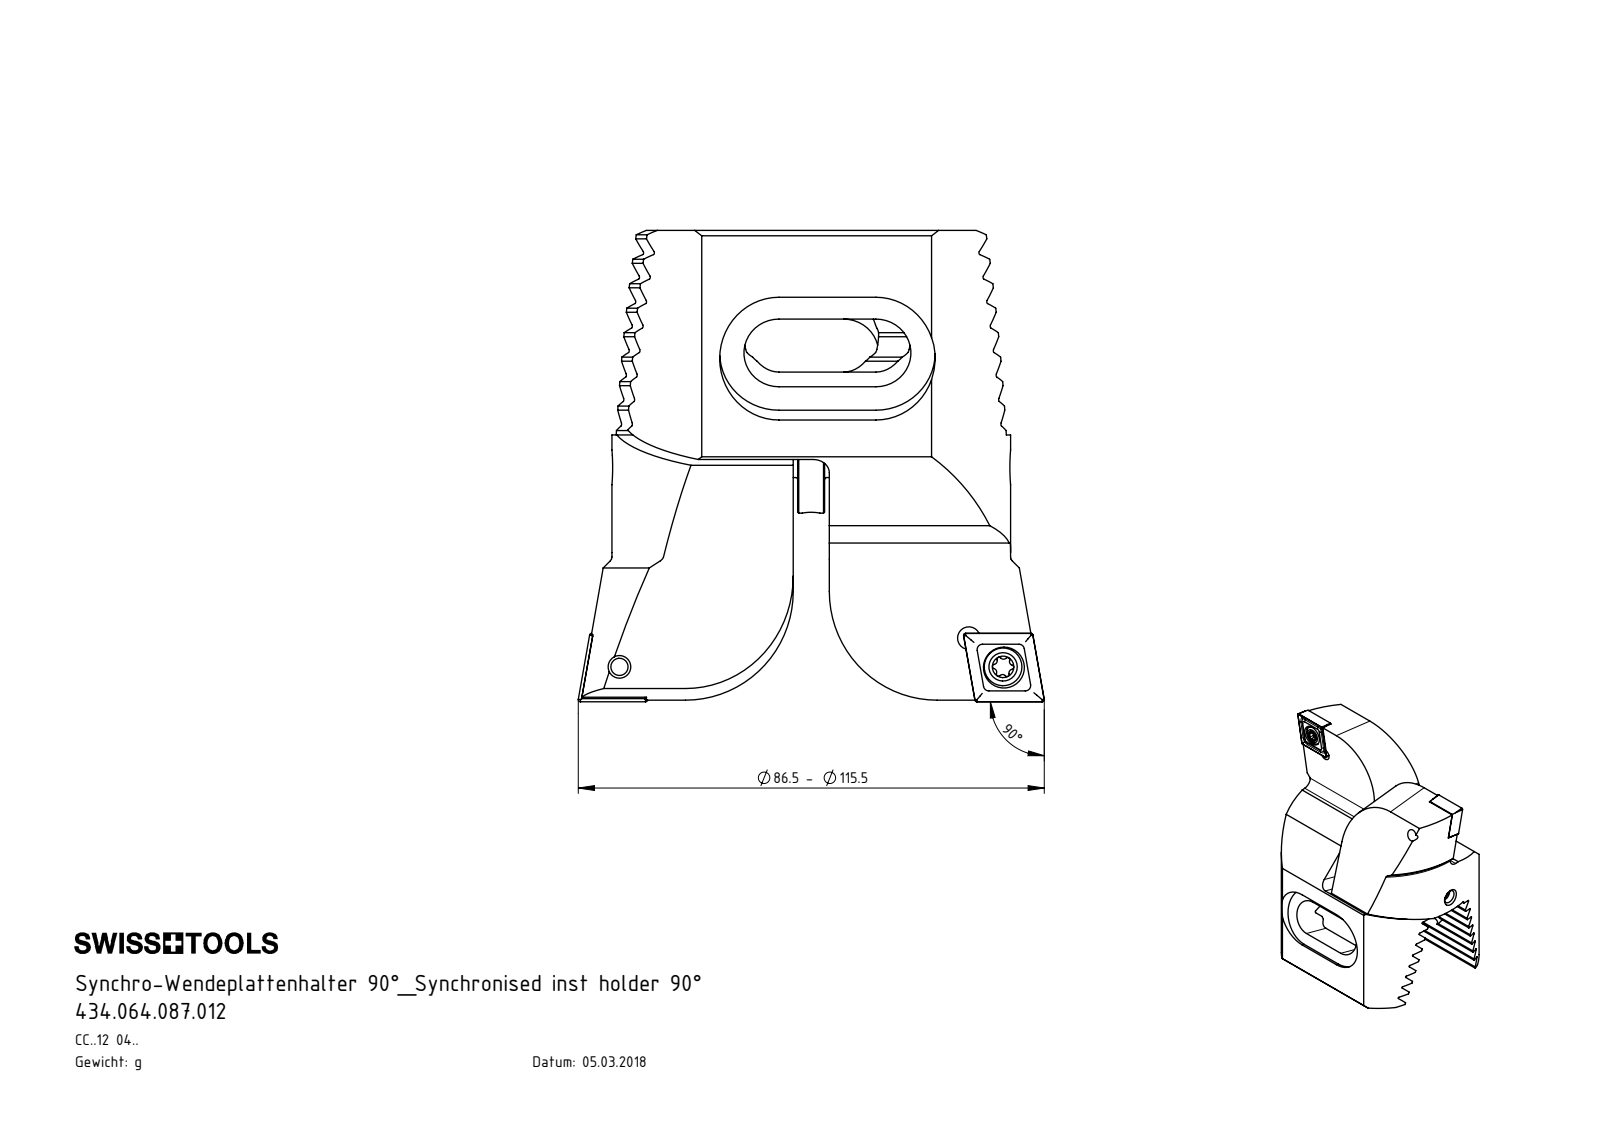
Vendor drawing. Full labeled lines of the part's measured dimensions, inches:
Part name (STEP PRODUCT): Z72-WCC.001.050_A; WCC-ER2.001.010_A; CCMT120404; Z72-ER3.001.068_A (+4 more)
STEP written by: SolidWorks 2017 (CONFIG_CONTROL_DESIGN)
Units: inches
Bodies: 11 solids, 499 faces (199 planar, 160 cylindrical, 140 other)
Overall size (bounding box): 3.443 × 3.406 × 2.283
Volume: 8.968 in³ · Surface area: 60.78 in²
Round holes (diameter × count): ⌀0.165 ×4, ⌀0.13 ×3, ⌀0.039 ×2, ⌀0.217 ×2, ⌀0.299 ×2, ⌀0.197 ×1
Round bosses / shafts (diameter × count): ⌀0.157 ×3, ⌀0.276 ×2, ⌀0.197 ×2, ⌀0.669 ×1, ⌀0.236 ×1, ⌀0.15 ×1
Partial cylindrical surfaces — rounded edges, fillets, slot ends (radius × count): R0.013 ×16, R0.015 ×12, R0.027 ×8, R0.039 ×8, R0.027 ×4, R0.118 ×4, R0.256 ×4, R0.433 ×4
Main face-to-face distances: 0.16, 0.32, 0.481, 0.641, 1.13, 1.154, 0.036, 0.962, 0.802, 2.283
Hole centre spacings: 0.327, 0.335, 0.591, 2.562, 2.569, 2.81, 1.141, 2.303
